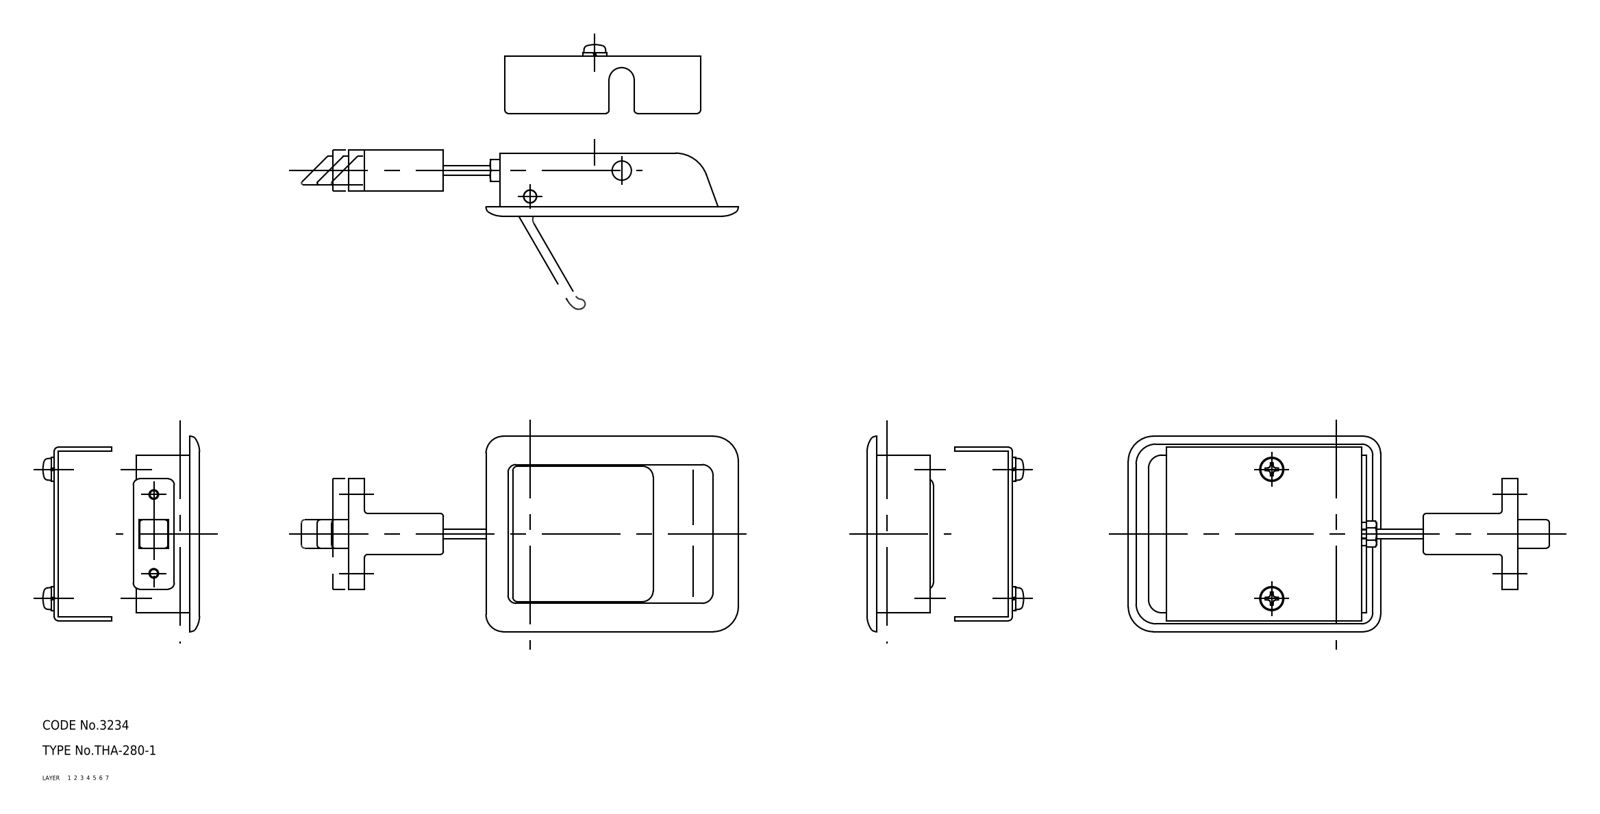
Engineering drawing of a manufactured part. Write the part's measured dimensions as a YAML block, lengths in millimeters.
part_name: "latch; case; screw; shaft (+7 more)"
step_written_by: "CADfix (AUTOMOTIVE_DESIGN)"
units: millimeters
bodies: {solids: 11, faces: 340, planar: 0, cylindrical: 0, other: 340}
overall_size: [133.5, 62, 27.05]
volume: 56336
surface_area: 44040
